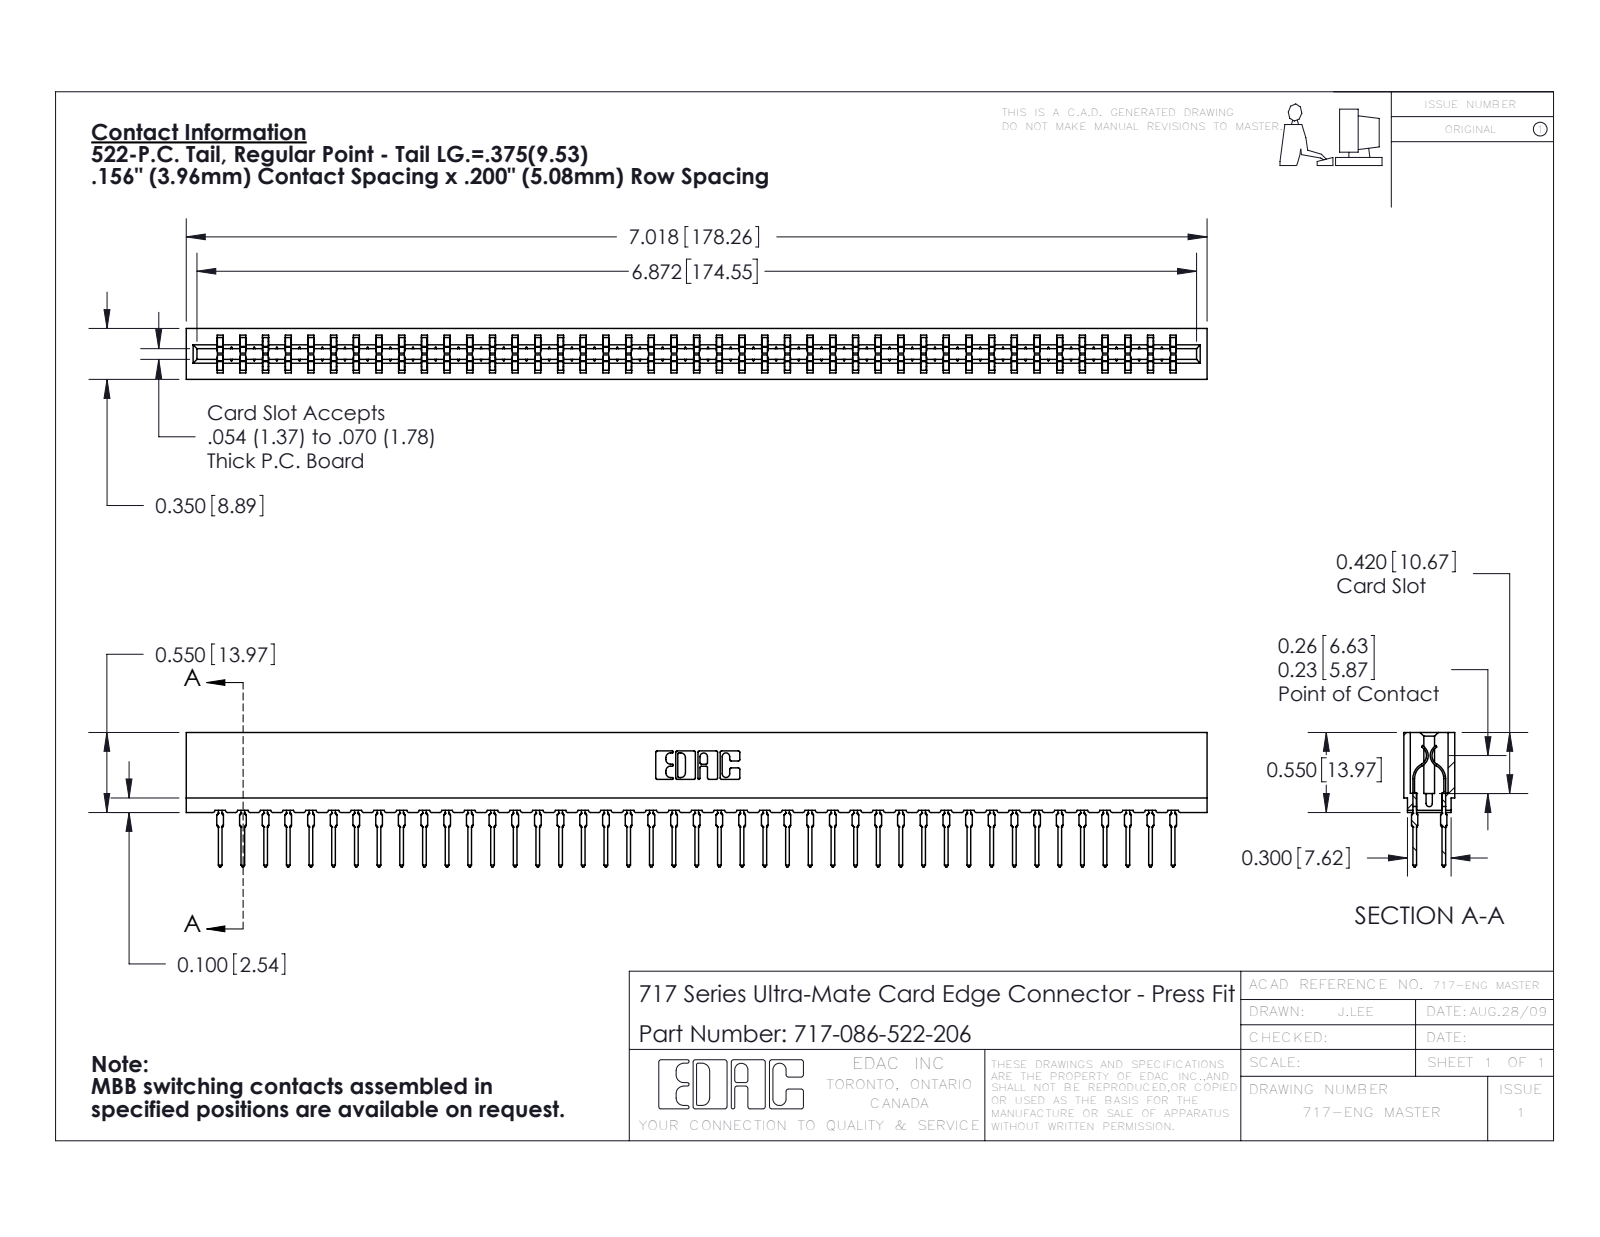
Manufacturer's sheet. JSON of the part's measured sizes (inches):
{"part_name": "745-292-001_522; 717 Part_Insulator Option - 06; 717-086-522-206", "step_written_by": "SolidWorks 2016 (CONFIG_CONTROL_DESIGN)", "units": "inches", "bodies": {"solids": 87, "faces": 7834, "planar": 4053, "cylindrical": 1545, "other": 2236}, "overall_size": [7.018, 0.924, 0.35], "volume_in3": 0.948, "surface_area_in2": 37.38, "partial_cylinders_radius": [[0.021, 172], [0.015, 86], [0.01, 22], [0.005, 8], [0.011, 8], [0.007, 6], [0.031, 6], [0.026, 3]], "face_to_face_distances": [0.212, 0.138, 0.35, 0.063, 0.287, 0.076, 0.149, 0.074, 0.045, 0.305]}
